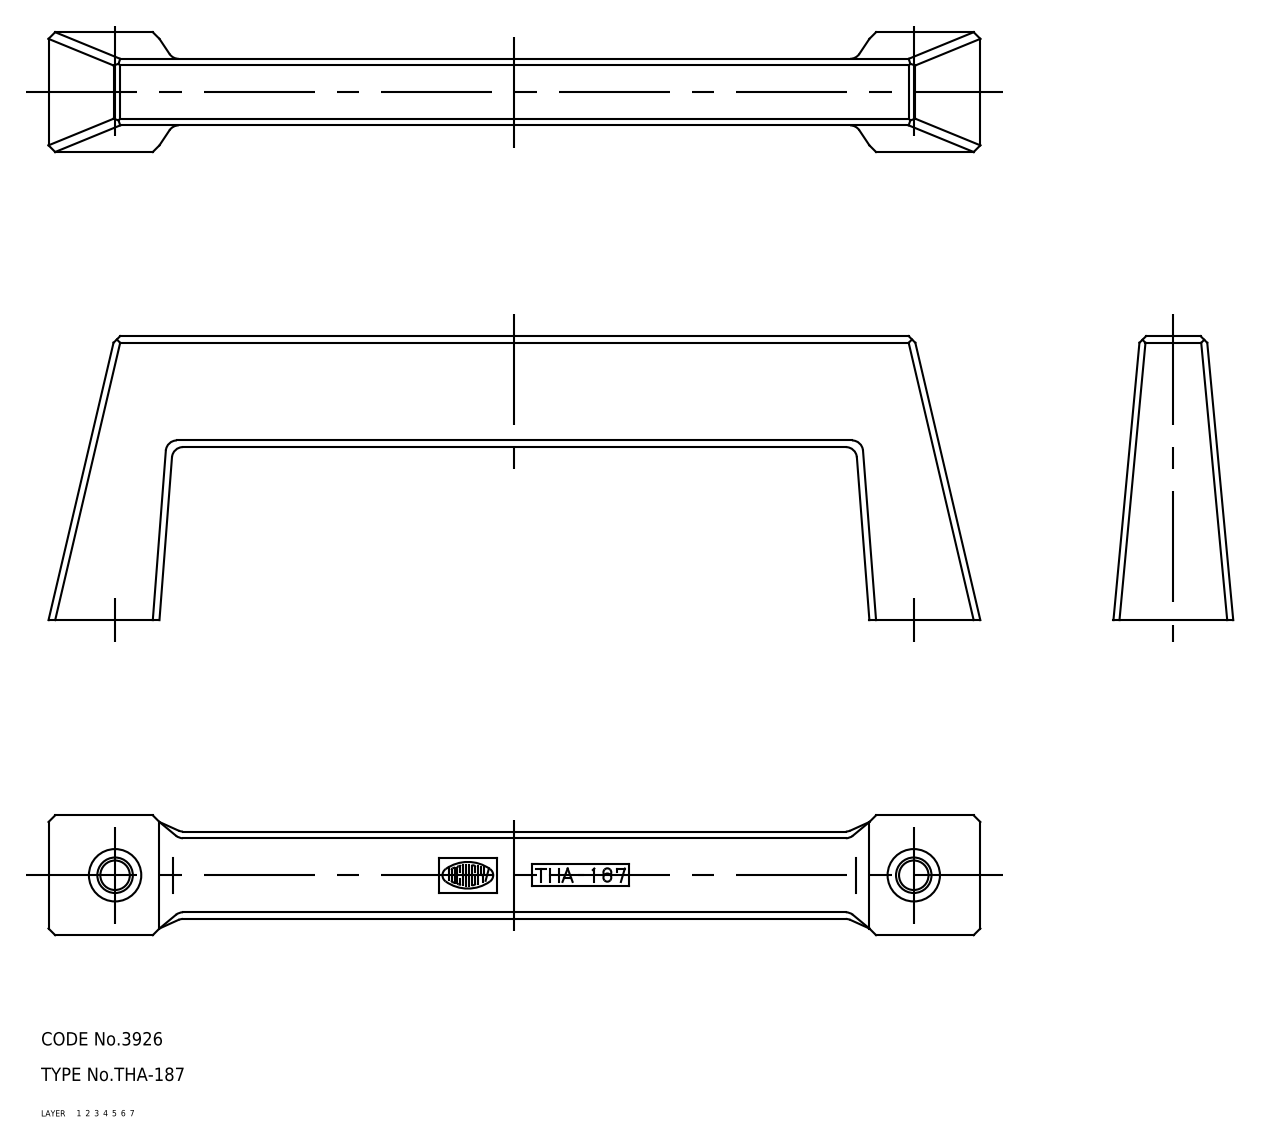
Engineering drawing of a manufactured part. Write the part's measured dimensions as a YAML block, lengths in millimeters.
part_name: "pull"
step_written_by: "CADfix (AUTOMOTIVE_DESIGN)"
units: millimeters
bodies: {solids: 1, faces: 40, planar: 0, cylindrical: 0, other: 40}
overall_size: [210, 64, 27]
volume: 117699
surface_area: 24431
